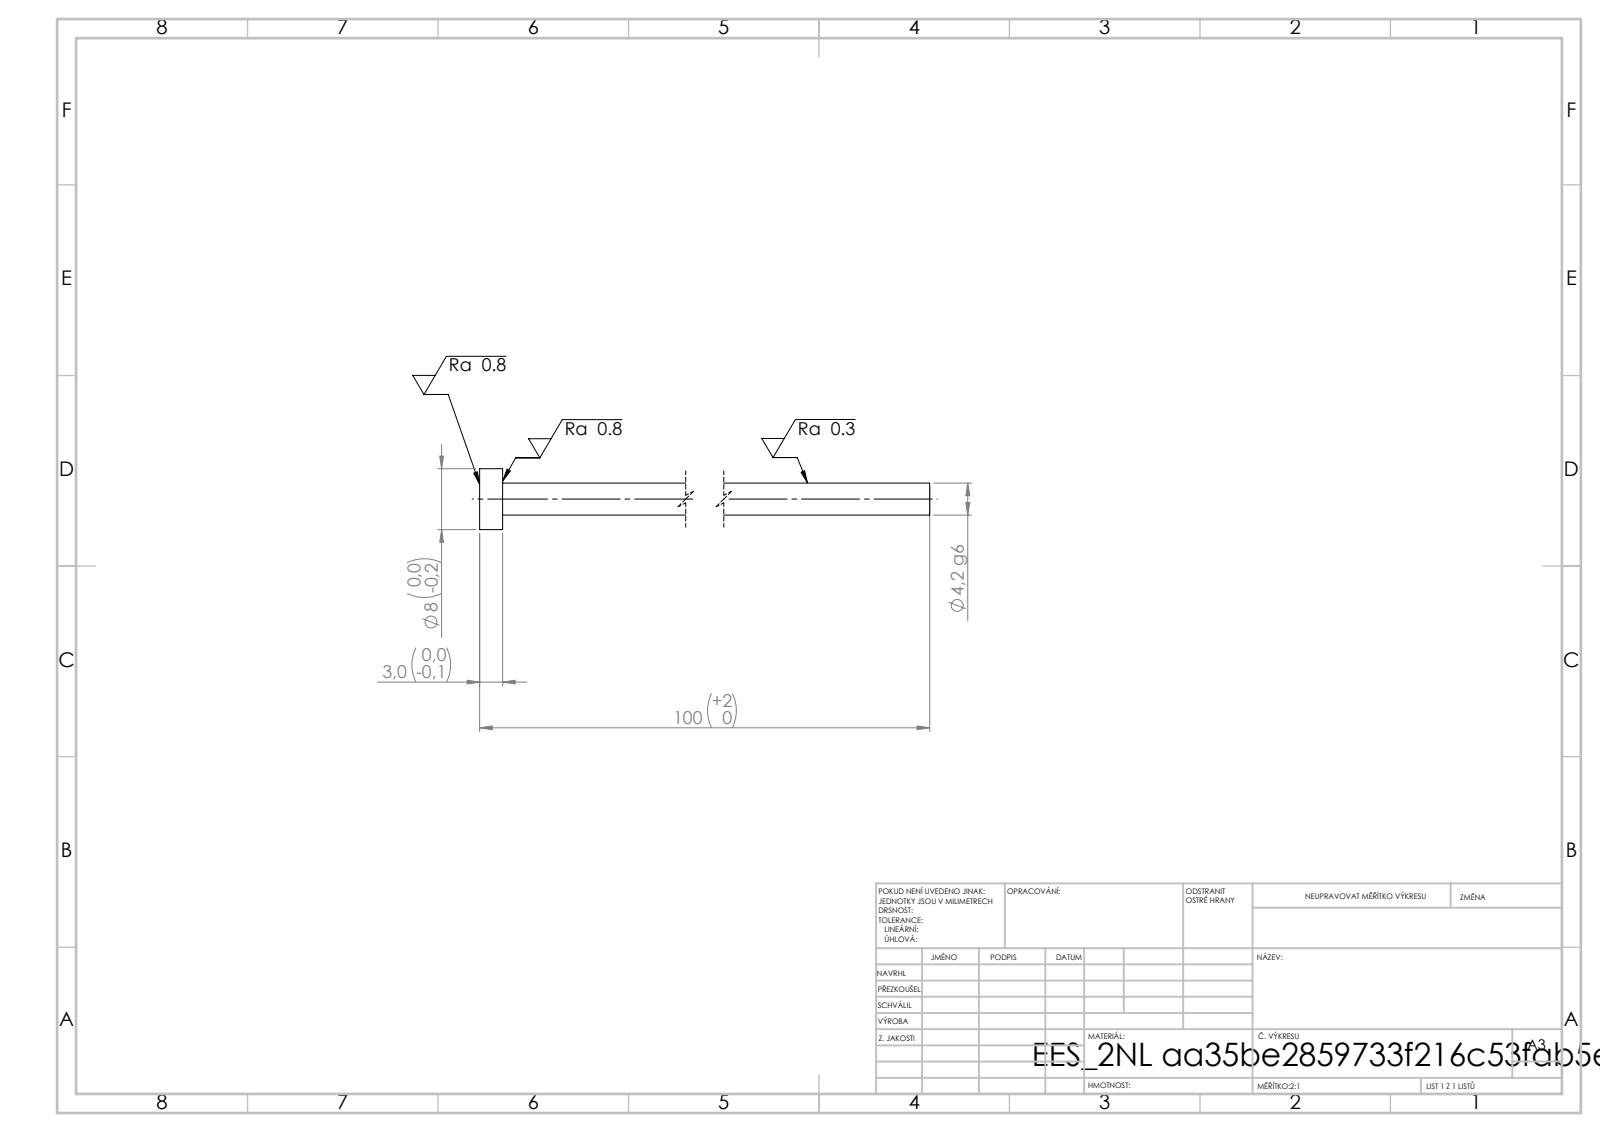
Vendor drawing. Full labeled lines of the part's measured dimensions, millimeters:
STEP written by: SolidWorks 2019 (CONFIG_CONTROL_DESIGN)
Units: millimetres
Bodies: 1 solid, 7 faces (3 planar, 4 cylindrical, 0 other)
Overall size (bounding box): 100 × 8 × 8
Volume: 1 495 mm³ · Surface area: 1 456 mm²
Round bosses / shafts (diameter × count): ⌀8 ×1, ⌀4.2 ×1
Main face-to-face distances: 3, 100, 97
